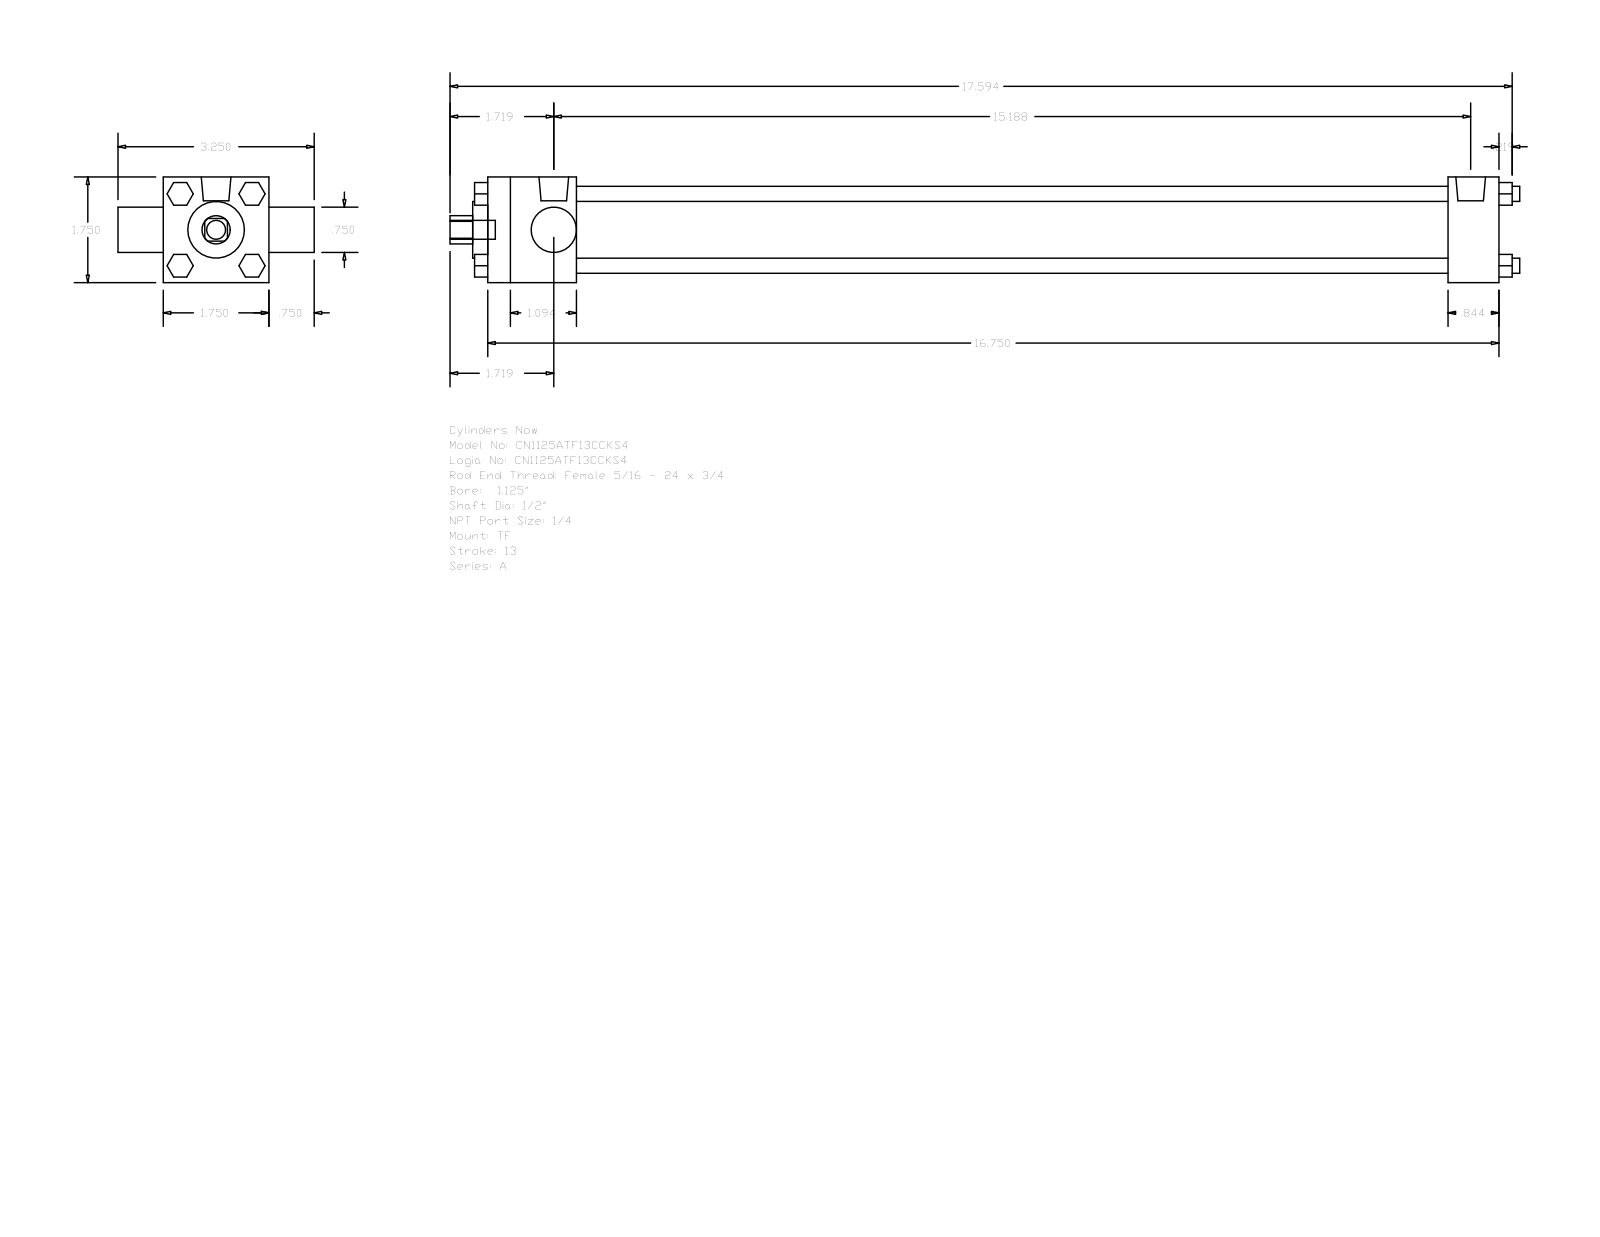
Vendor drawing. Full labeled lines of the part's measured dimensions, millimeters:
Part name (STEP PRODUCT): A_TF__0112_0.5
STEP written by: GSSL Pune (CONFIG_CONTROL_DESIGN)
Units: millimetres
Bodies: 0 solids, 120 faces (92 planar, 28 cylindrical, 0 other)
Overall size (bounding box): 450.06 × 82.55 × 44.45
Round holes (diameter × count): ⌀12.7 ×1, ⌀19.05 ×1, ⌀23.81 ×1, ⌀31.88 ×1
Round bosses / shafts (diameter × count): ⌀6.35 ×4, ⌀5.56 ×3, ⌀12.49 ×2, ⌀7.94 ×1
Partial cylindrical surfaces — rounded edges, fillets, slot ends (radius × count): R5.94 ×1
Main face-to-face distances: 44.46, 425.44, 404.01, 21.43, 37.3, 366.71, 388.14, 19.04, 63.5, 9.53
